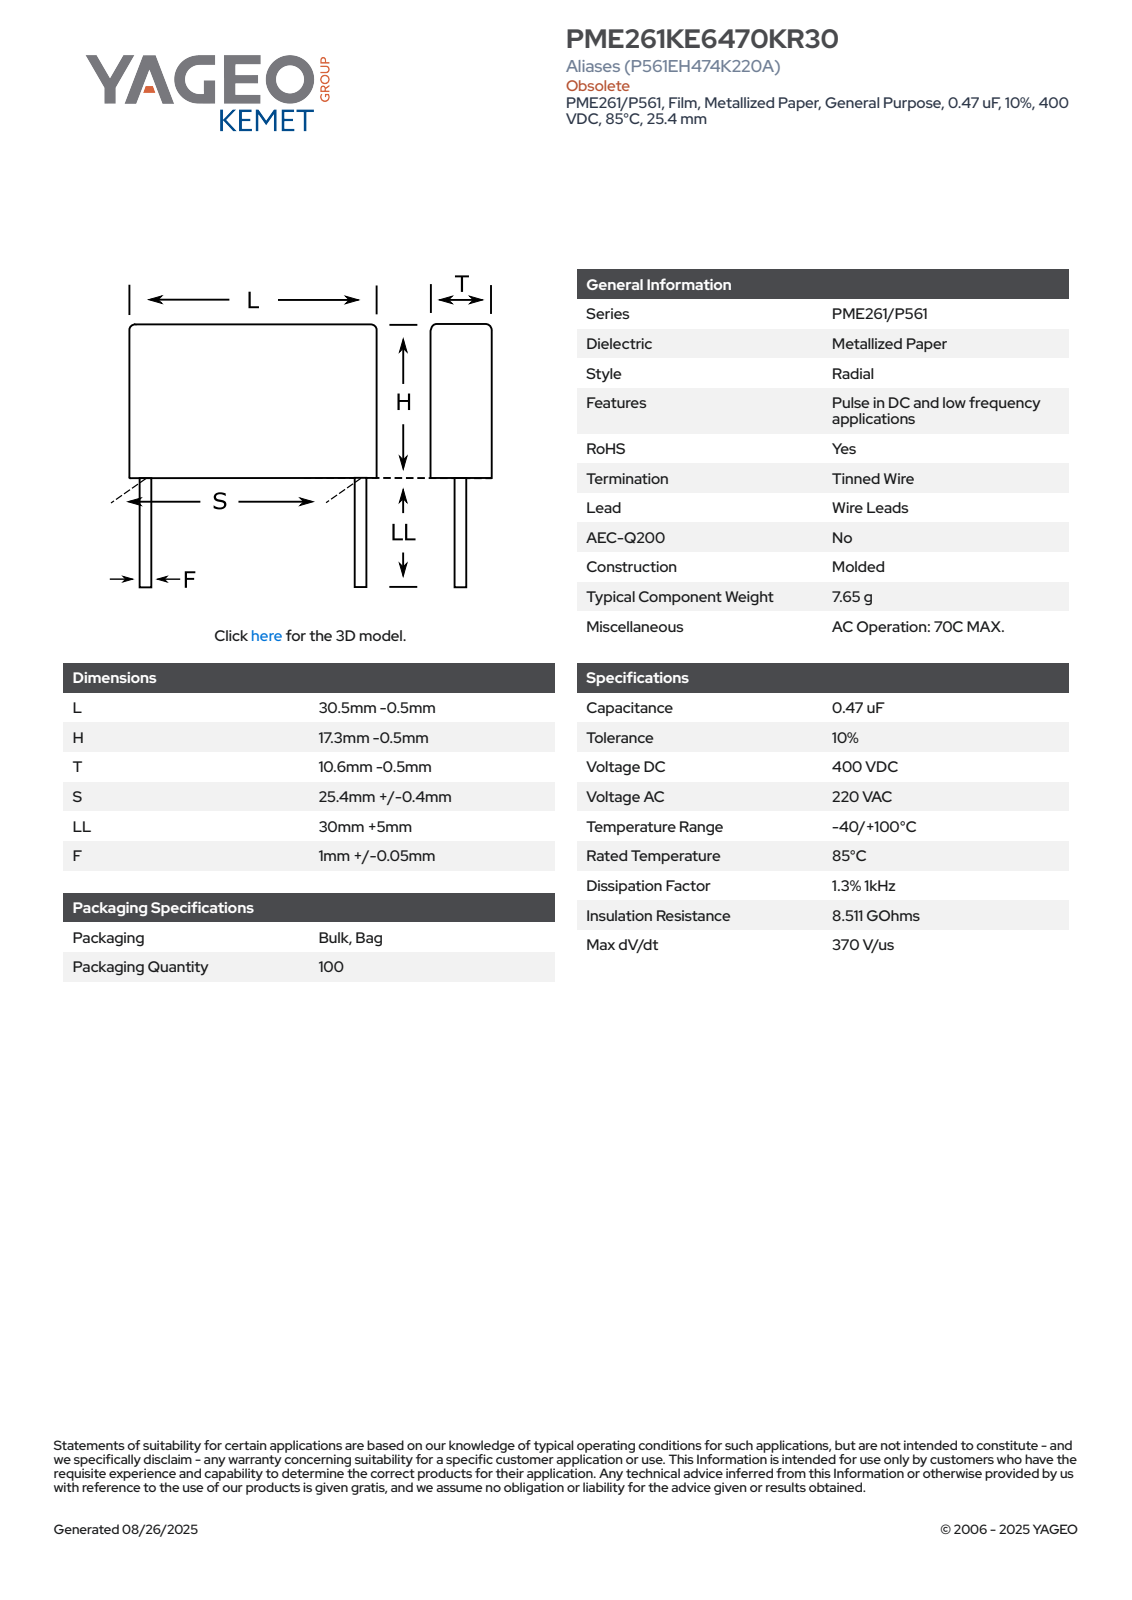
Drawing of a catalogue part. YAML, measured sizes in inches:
part_name: "CFR_MOLDED_30.5X17.3X10.6_L30H16.8T10.1S25.4LL35F1.05"
step_written_by: "SolidWorks 2014 (AUTOMOTIVE_DESIGN)"
units: inches
bodies: {solids: 4, faces: 73, planar: 65, cylindrical: 8, other: 0}
overall_size: [2.039, 1.181, 0.398]
volume: 0.314
surface_area: 3.426
round_bosses_or_shafts:
  - {diameter: 0.041, count: 2}
partial_cylinders:
  - {radius: 0.02, count: 4}
face_to_face_distances: [0.398, 0.661, 1.181, 1.378, 2.039, 1.761, 0.383, 0.278, 1.655, 0.277]
